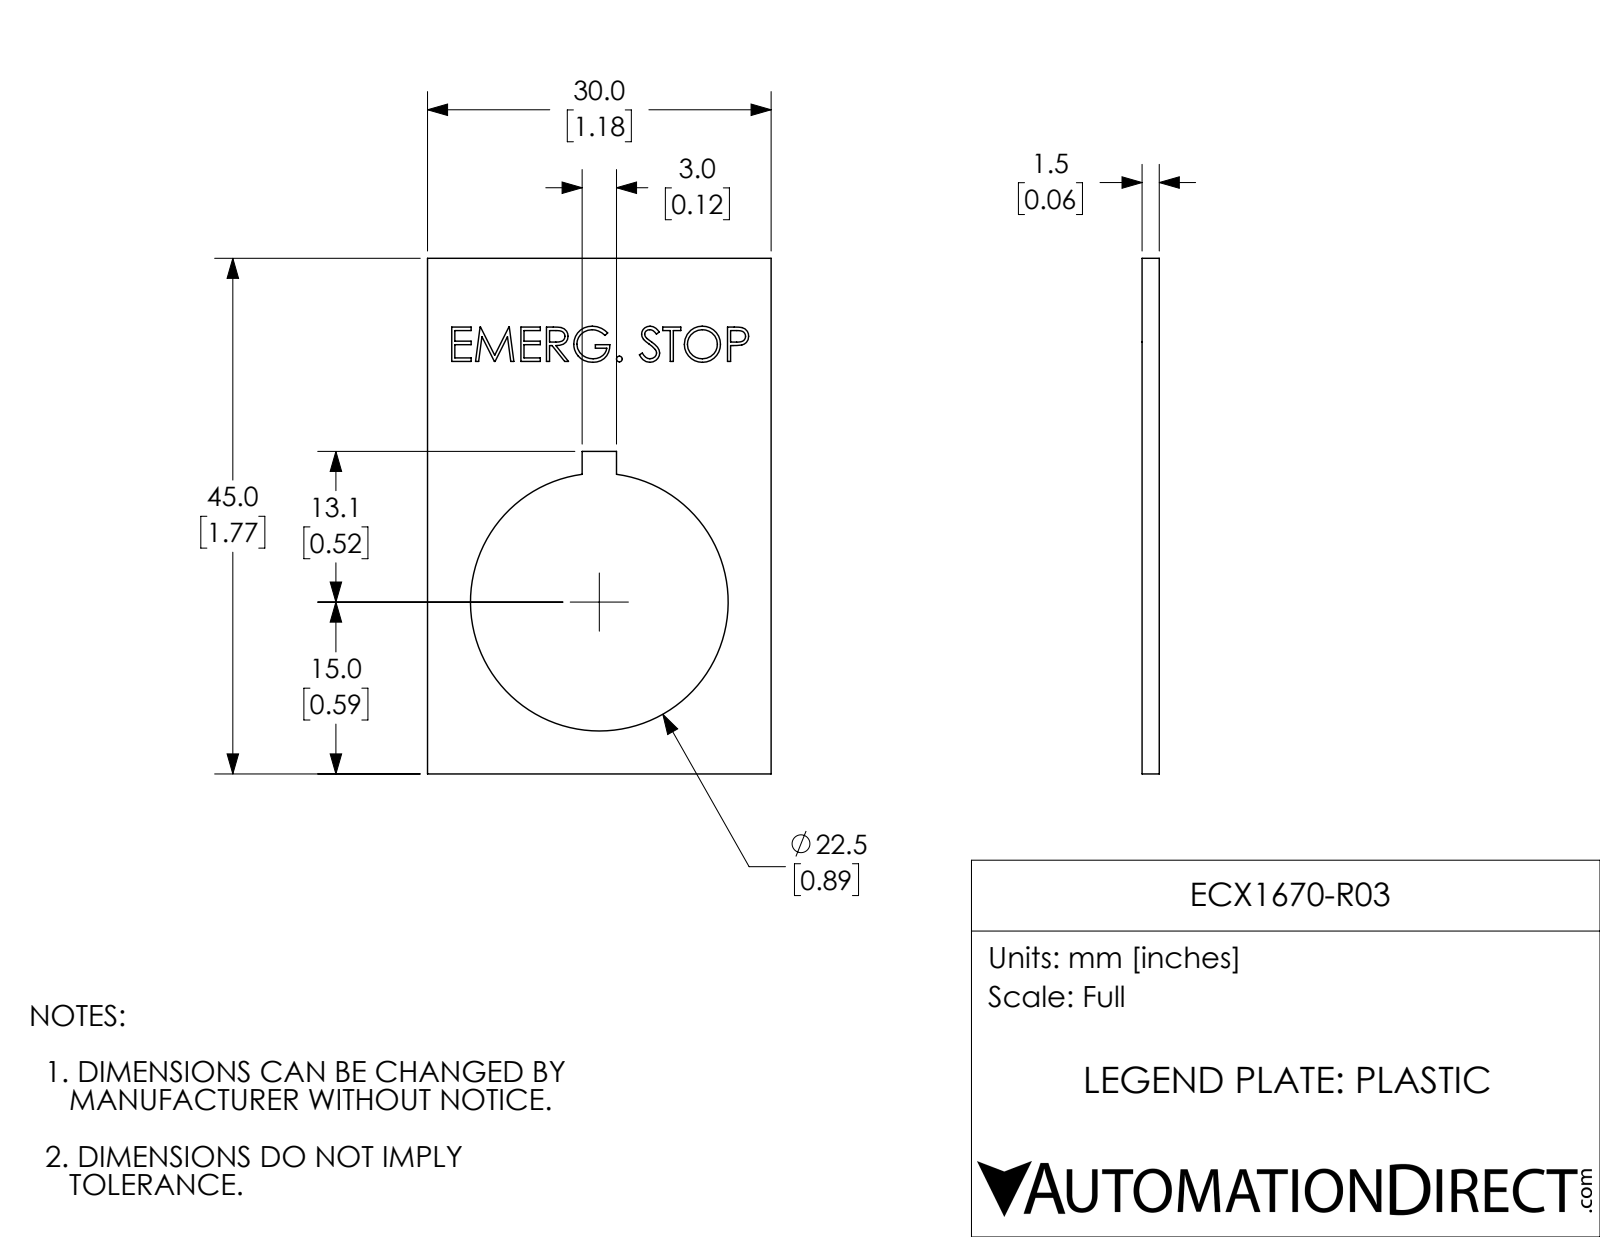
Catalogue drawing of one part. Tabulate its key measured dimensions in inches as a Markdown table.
| quantity | value |
| --- | --- |
| part name | ECX1670-R03 |
| STEP written by | SolidWorks 2017 (AUTOMOTIVE_DESIGN) |
| units | inches |
| bodies | 1 solid, 142 faces (92 planar, 3 cylindrical, 47 other) |
| overall size | 1.772 × 1.181 × 0.059 |
| volume | 0.087 in³ |
| surface area | 3.462 in² |
| round holes (diameter × count) | 0.886 × 1 |
| main face-to-face distances | 0.059, 1.181, 1.772, 0.058, 0.531, 0.65, 1.108, 0.663, 0.118, 0.012 |
